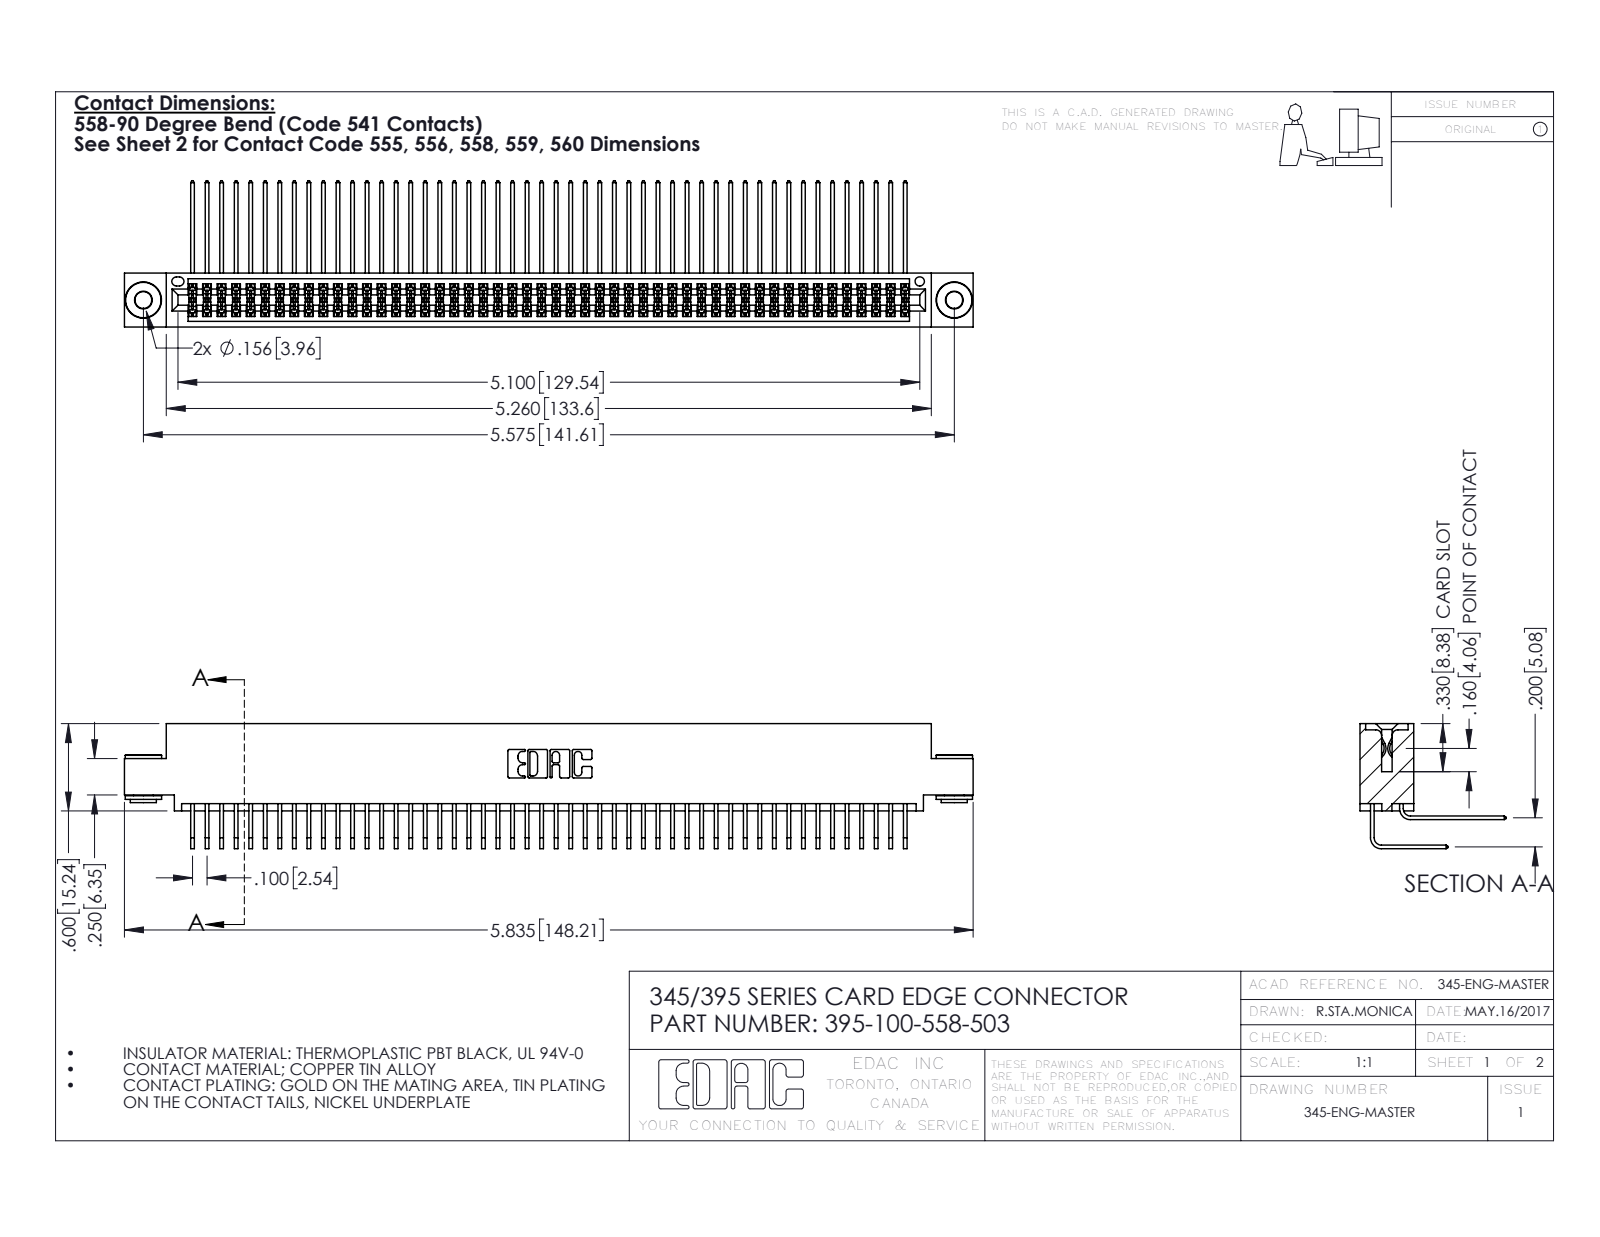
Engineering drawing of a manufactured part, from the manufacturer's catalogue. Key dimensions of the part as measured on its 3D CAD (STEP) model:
Part name (STEP PRODUCT): 345-250-002_345-250-002-102; 345-292-001_558 559 Tail - 1; 345-292-001_558 Tail - 2; 395-100-558-503 (+1 more)
STEP written by: SolidWorks 2016 (CONFIG_CONTROL_DESIGN)
Units: inches
Bodies: 103 solids, 5368 faces (3594 planar, 1766 cylindrical, 8 other)
Overall size (bounding box): 5.835 × 1.005 × 0.859
Volume: 0.915 in³ · Surface area: 39.26 in²
Round holes (diameter × count): ⌀0.116 ×2, ⌀0.156 ×2, ⌀0.064 ×1
Round bosses / shafts (diameter × count): ⌀0.25 ×2, ⌀0.18 ×2, ⌀0.136 ×2
Partial cylindrical surfaces — rounded edges, fillets, slot ends (radius × count): R0.006 ×151, R0.01 ×22, R0.007 ×6, R0.031 ×6, R0.026 ×3, R0.014 ×2, R0.019 ×2, R0.022 ×2
Main face-to-face distances: 0.072, 0.298, 0.2, 0.025, 0.37, 0.098, 0.272, 0.225, 0.025, 0.175
Hole centre spacings: 0.27, 5.339, 5.575
